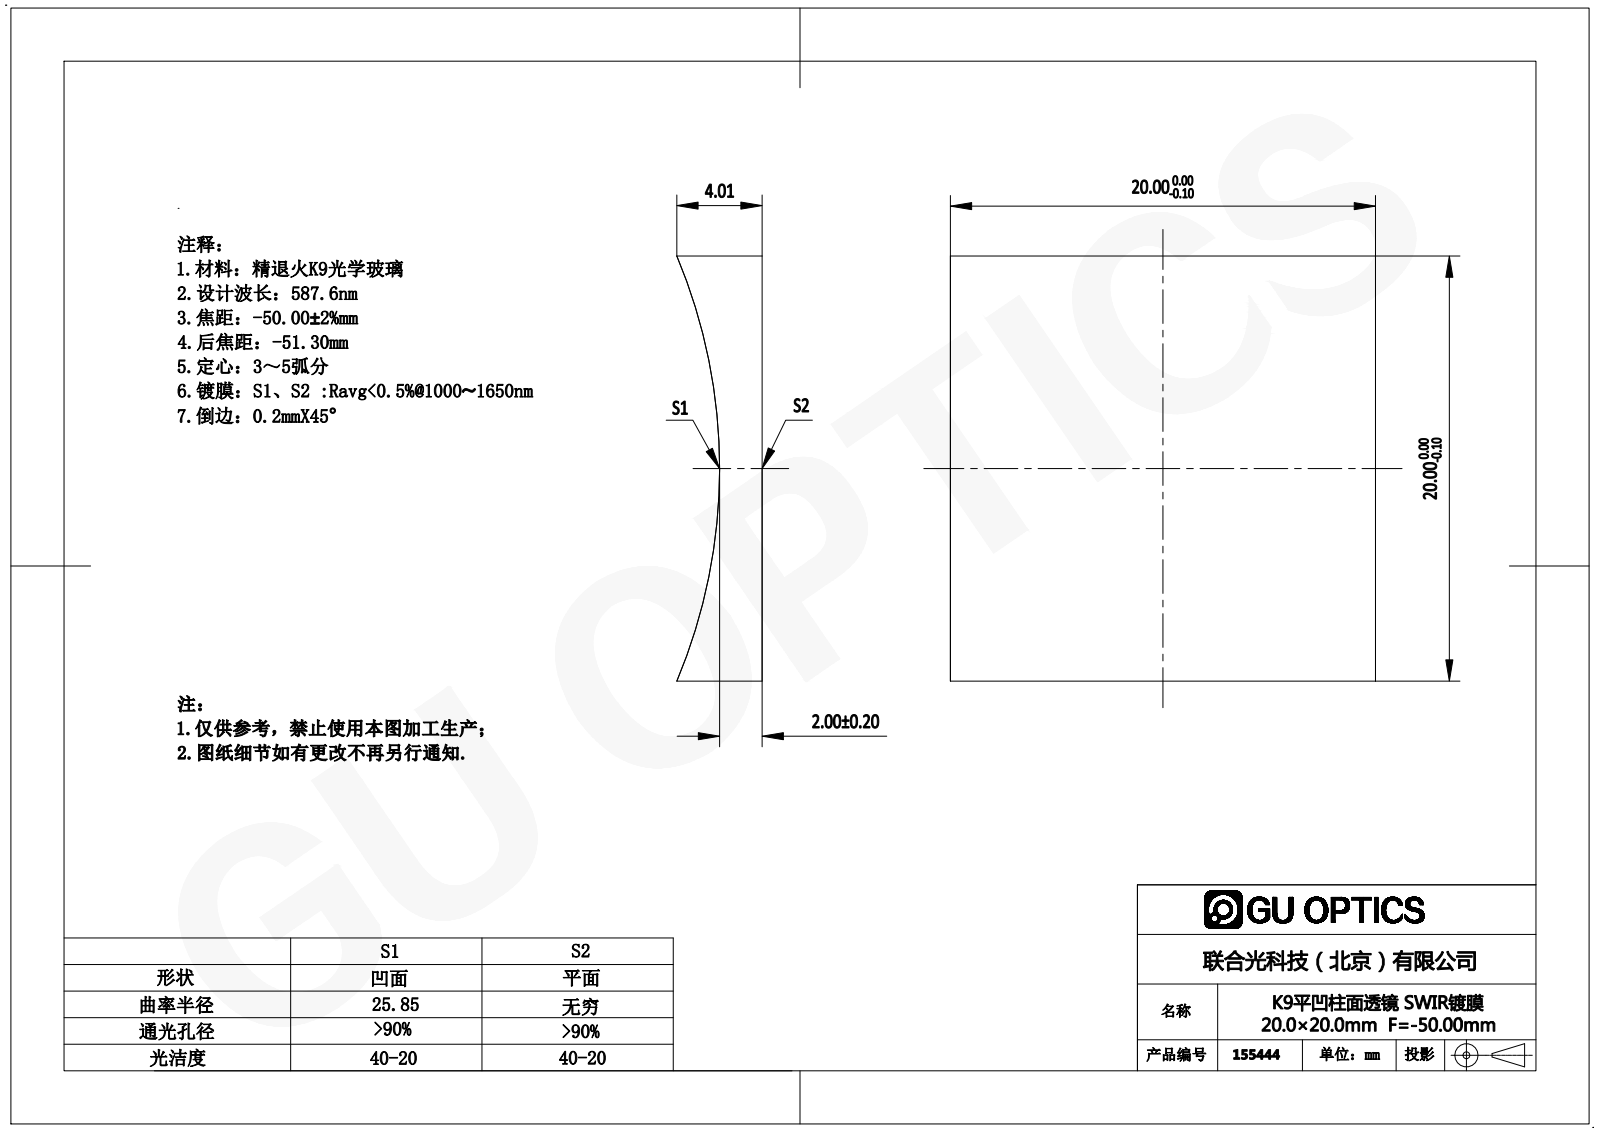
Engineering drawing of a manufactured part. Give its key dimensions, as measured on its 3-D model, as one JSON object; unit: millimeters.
{"part_name": "155345", "step_written_by": "SolidWorks 2016 (AUTOMOTIVE_DESIGN)", "units": "millimeters", "bodies": {"solids": 1, "faces": 6, "planar": 5, "cylindrical": 1, "other": 0}, "overall_size": [20, 20, 4.01], "volume_mm3": 1064, "surface_area_mm2": 1078, "partial_cylinders_radius": [[25.85, 1]], "face_to_face_distances": [20]}
